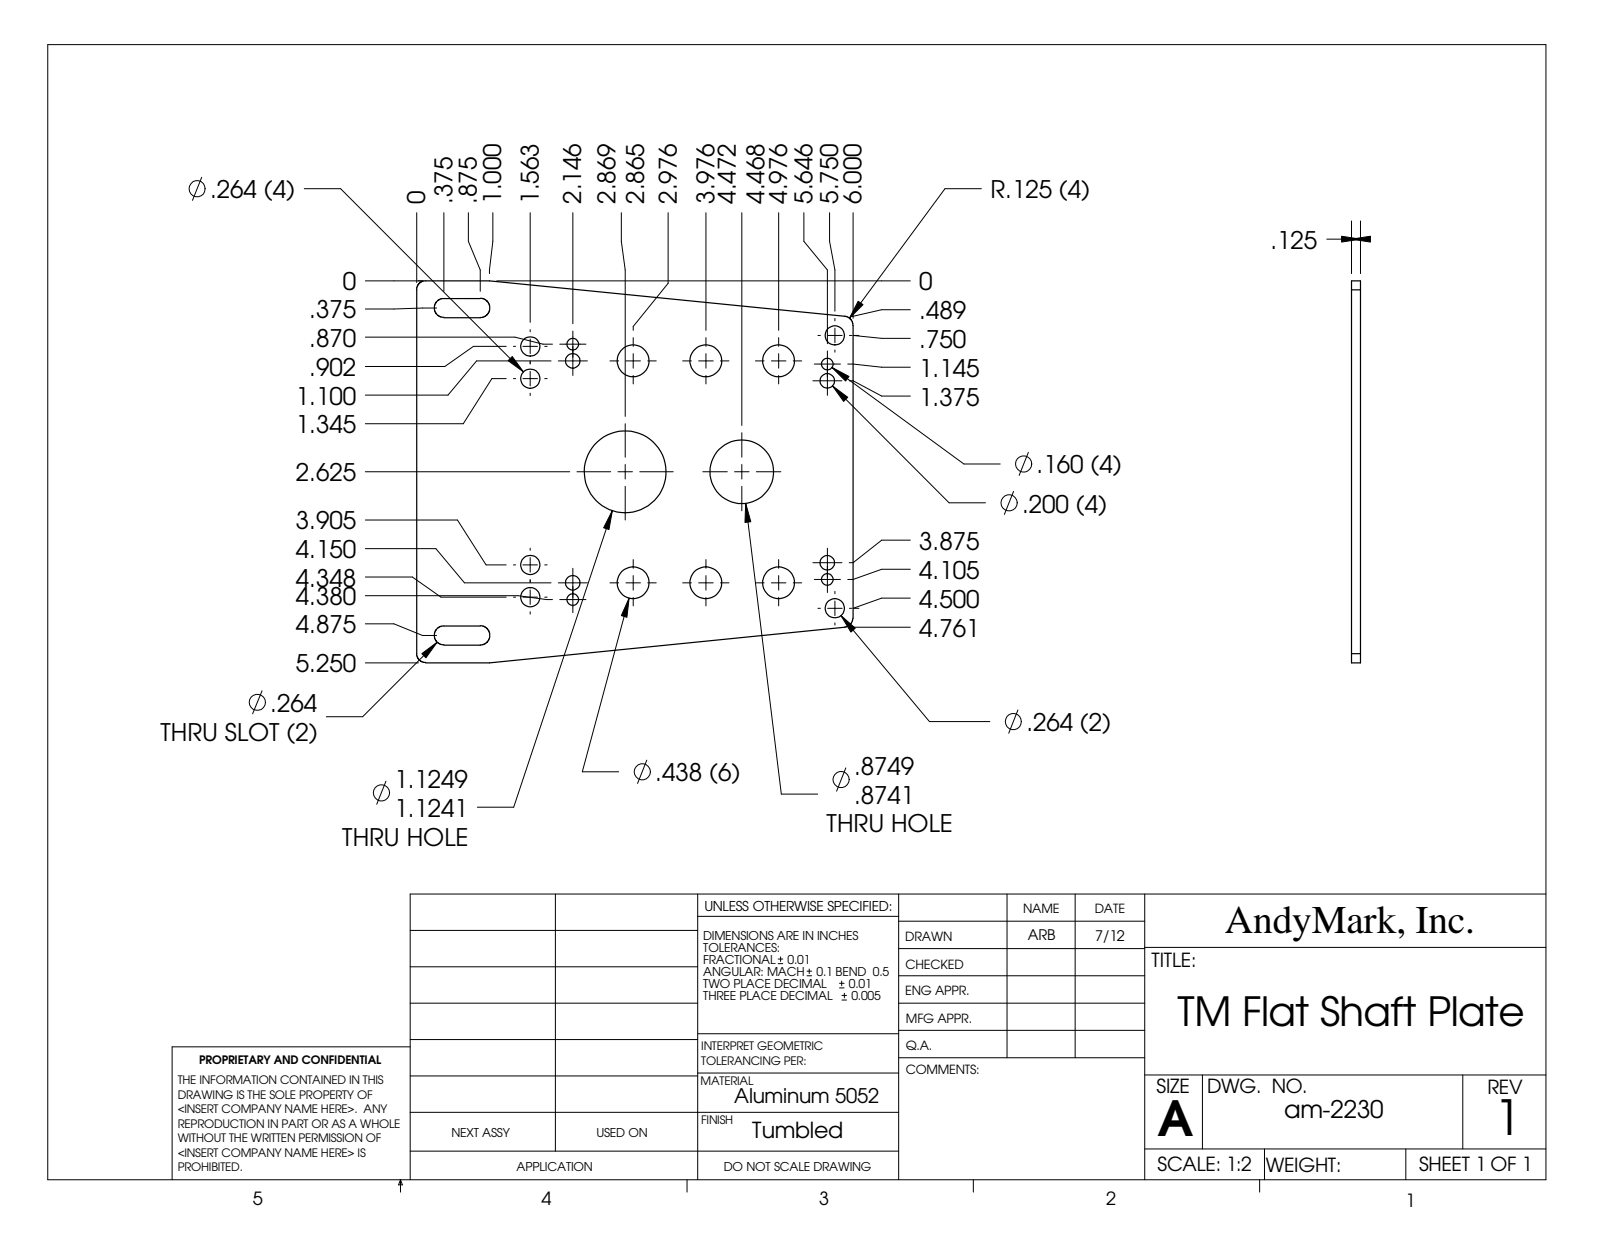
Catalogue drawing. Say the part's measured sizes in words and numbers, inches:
The part is named "am-2230 TM Flat Shaft Plate". Its 3-D file was written by "SolidWorks 2014 (AUTOMOTIVE_DESIGN)". It is 1 solid with 64 faces: 12 planar, 52 cylindrical and 0 other. Overall it measures 6 by 5.25 by 0.125 inches. Its volume is 3.198 cubic inches and its surface area 57.3 square inches. Round holes: 6 of diameter 0.264, 6 of diameter 0.437, 4 of diameter 0.16, 4 of diameter 0.2, 1 of diameter 0.874, 1 of diameter 1.124. Partial cylindrical surfaces (rounded edges, fillets, slot ends): 4 of radius 0.125, 4 of radius 0.132. The main face-to-face distances are 0.125, 6, 0.243, 0.507, 4.743, 5.007, 4.5, 0.264, 5.25, 4.764. The hole center spacings are 1, 3.05, 3.21, 3.511, 4.613, 0.23, 0.408, 0.443.
